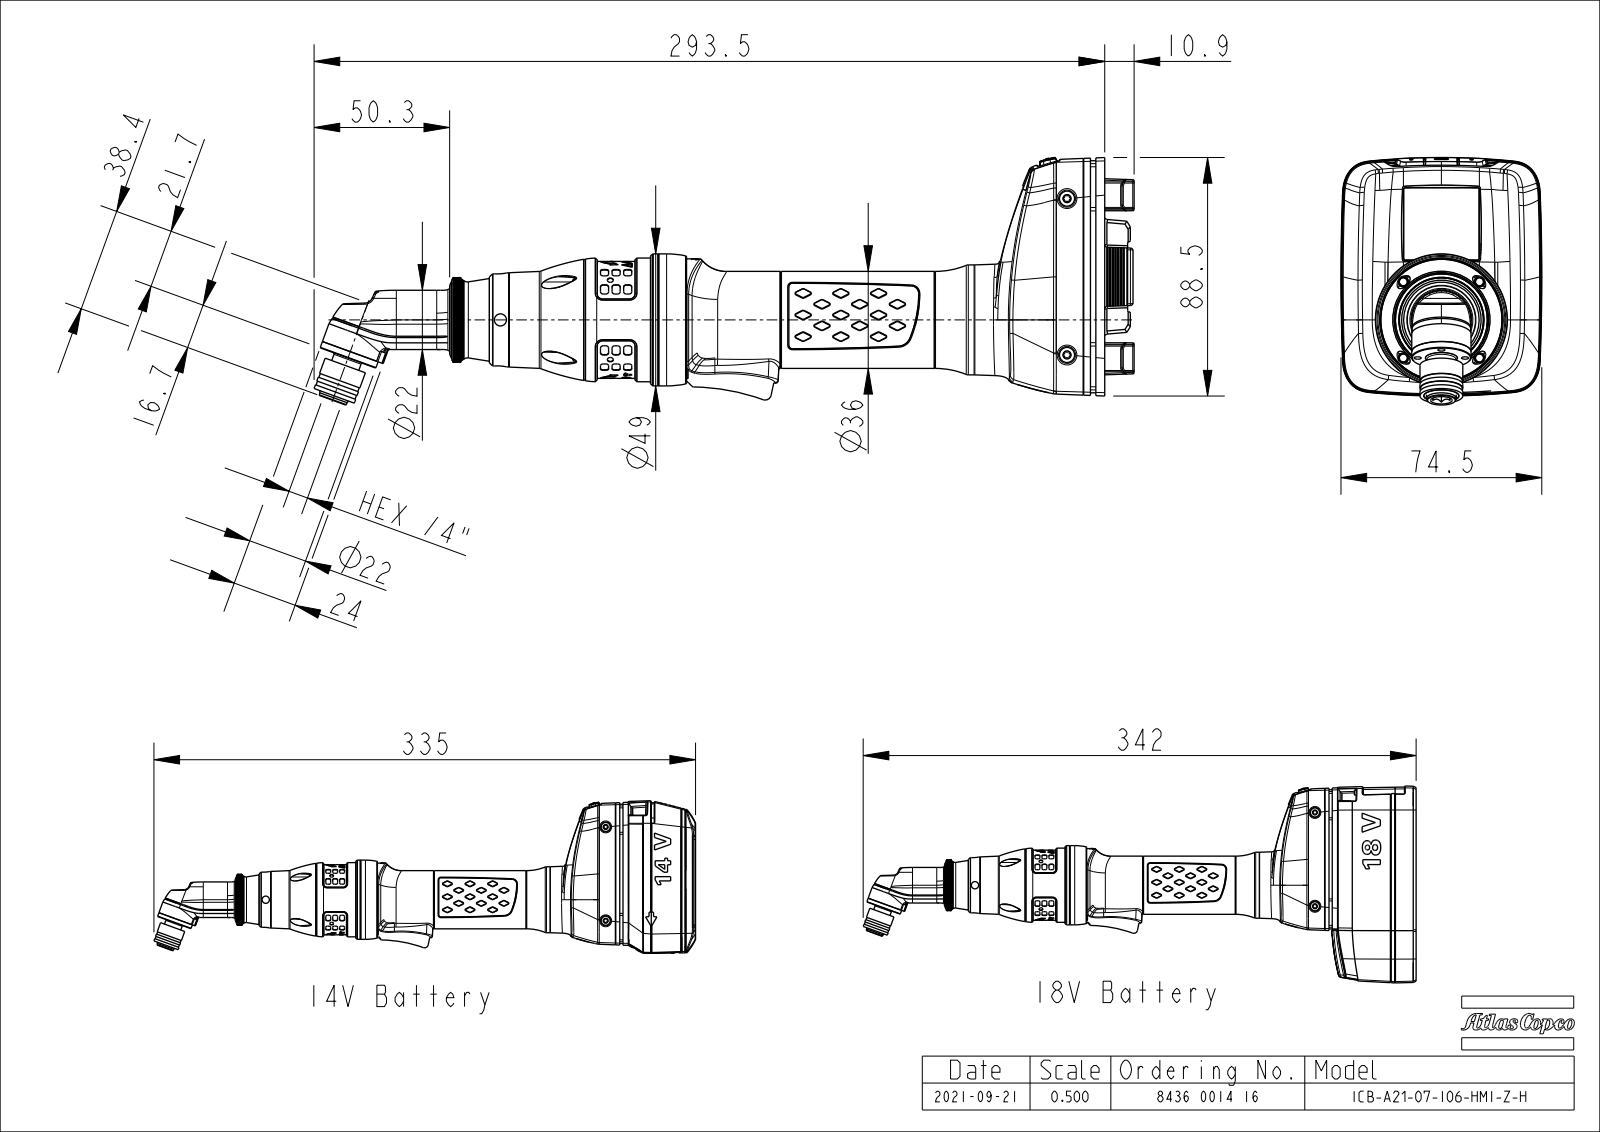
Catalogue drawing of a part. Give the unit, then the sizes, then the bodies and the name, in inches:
Units: inches
Overall size (bounding box): 11.985 × 3.543 × 2.936
Round holes (diameter × count): ⌀0.102 ×4, ⌀0.126 ×4, ⌀0.138 ×2, ⌀0.177 ×2, ⌀0.128 ×1, ⌀0.421 ×1, ⌀0.472 ×1, ⌀0.551 ×1
Round bosses / shafts (diameter × count): ⌀0.315 ×4, ⌀0.22 ×4, ⌀0.118 ×4, ⌀1.929 ×1, ⌀1.807 ×1, ⌀1.783 ×1, ⌀1.606 ×1, ⌀1.417 ×1
Partial cylindrical surfaces — rounded edges, fillets, slot ends (radius × count): R0.012 ×428, R0.02 ×258, R0.039 ×64, R0.004 ×38, R0.015 ×24, R0.02 ×24, R0.027 ×24, R0.011 ×22
Main face-to-face distances: 4.744, 4.743, 0.098, 0.797, 0.197, 0.413, 0.118, 5.156, 5.157, 0.209
Hole centre spacings: 0.346, 0.49, 0.693, 2.283, 2.283, 2.284
Volume: 28.88 in³ · Surface area: 111 in²
Bodies: 7 solids, 11343 faces (7095 planar, 1651 cylindrical, 2597 other)
Part name (STEP PRODUCT): EXT_COMP_SW0085
STEP written by: CREO PARAMETRIC BY PTC INC, 2020281 (CONFIG_CONTROL_DESIGN)
